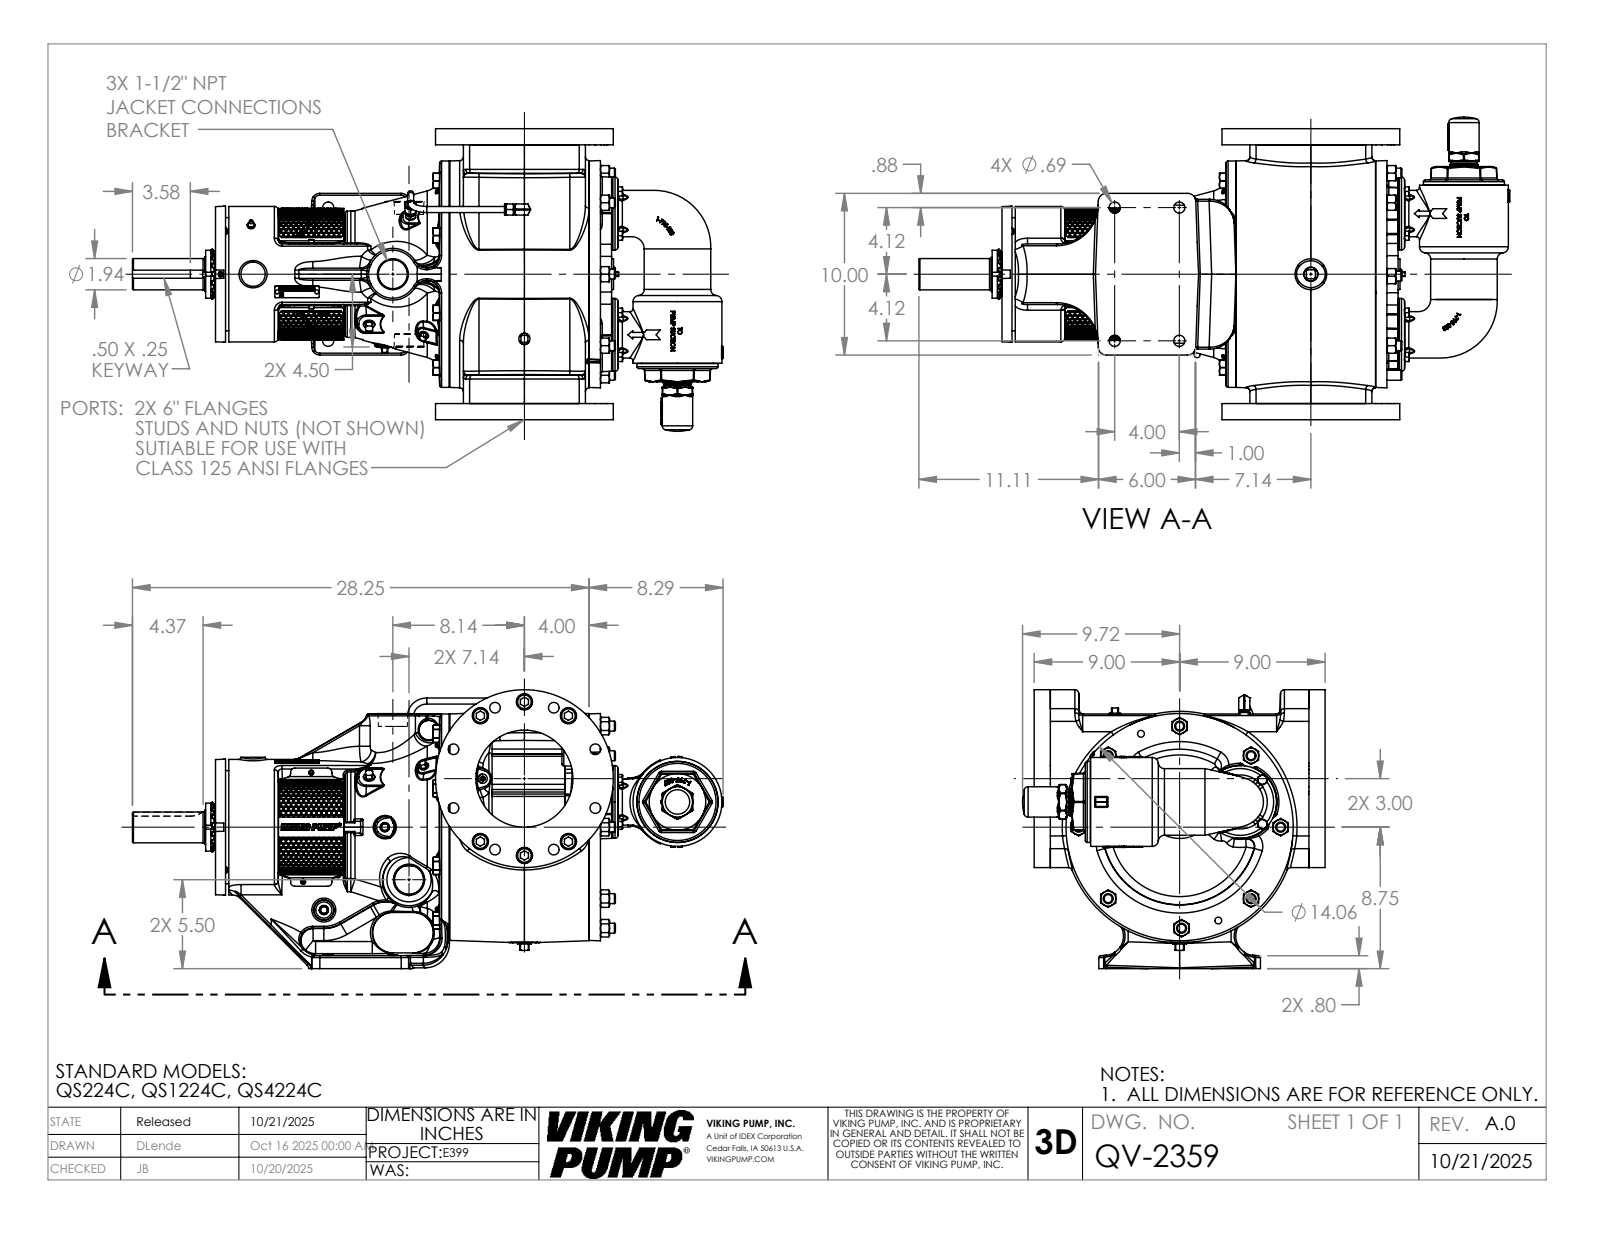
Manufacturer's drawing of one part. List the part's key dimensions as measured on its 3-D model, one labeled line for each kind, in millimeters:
Part name (STEP PRODUCT): QV-2359
STEP written by: SolidWorks 2024 (AUTOMOTIVE_DESIGN)
Units: millimetres
Bodies: 1 solid, 4941 faces (1631 planar, 798 cylindrical, 2512 other)
Overall size (bounding box): 928.2 × 475.5 × 438.2
Volume: 49 720 000 mm³ · Surface area: 1 665 000 mm²
Round holes (diameter × count): ⌀6.4 ×9, ⌀6.8 ×8, ⌀10.3 ×8, ⌀10.4 ×8, ⌀16.7 ×8, ⌀29.4 ×8, ⌀25.4 ×6, ⌀17.5 ×4, ⌀22.2 ×4, ⌀4 ×2, ⌀8 ×2, ⌀10.7 ×2
Round bosses / shafts (diameter × count): ⌀9.5 ×12, ⌀15.7 ×8, ⌀23.8 ×6, ⌀7.9 ×3, ⌀4.8 ×3, ⌀114.3 ×2, ⌀17.4 ×2, ⌀14.3 ×2
Partial cylindrical surfaces — rounded edges, fillets, slot ends (radius × count): R3 ×60, R19.1 ×22, R1.5 ×20, R0.4 ×18, R2.3 ×18, R1.8 ×16, R0.8 ×13, R12.7 ×12
Main face-to-face distances: 25.4, 431.8, 457.2, 406.4, 14.5, 605, 97, 507.9, 565.6, 202.5
Hole centre spacings: 95.3, 52.8, 120.7, 146.9, 68.9, 96.2, 137.7, 79.6
